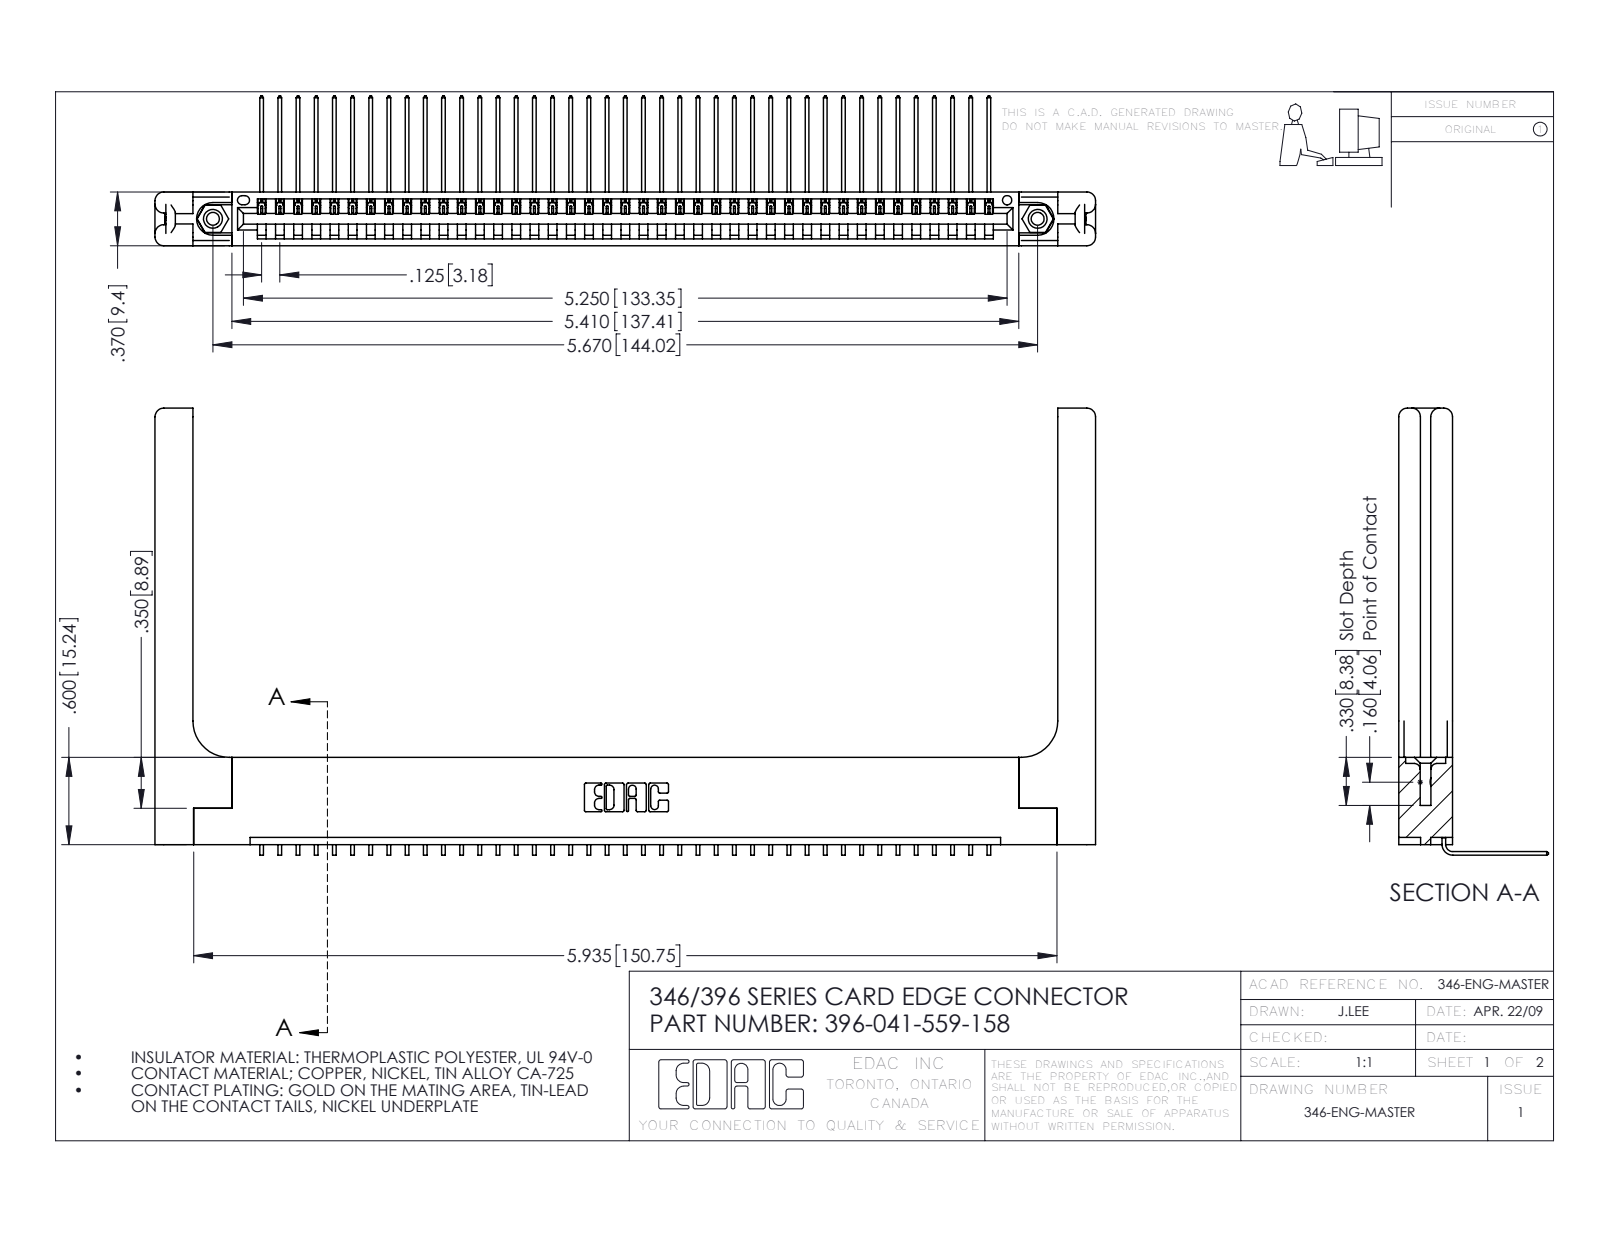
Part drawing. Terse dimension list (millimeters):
name: 396-041-559-158; 346 Part_Flush Mounting Lugs - 0.156 Dia-TH; 345-292-001_558 559 Tail - 1; 346-220-058_345-220-058 (+1 more)
written by: SolidWorks 2016 (CONFIG_CONTROL_DESIGN)
unit: mm
bodies: 46 solids, 2838 faces (1946 planar, 832 cylindrical, 60 other)
size: 164.2 × 78.1 × 26.2
volume: 23 370 mm³; area: 25 790 mm²
holes: 2× ⌀2.3, 2× ⌀3.2, 2× ⌀4, 1× ⌀1.6
bosses: 2× ⌀3.9
rounds: 82× R0.2, 22× R0.3, 16× R1.5, 6× R0.2, 6× R0.8, 3× R0.7, 2× R0.8, 2× R0.8
face distances: 9.4, 1.2, 8.2, 1.8, 3.8, 3.8, 0.6, 6.4, 7.6, 5.6
hole spacings: 6.2, 138.7, 144
